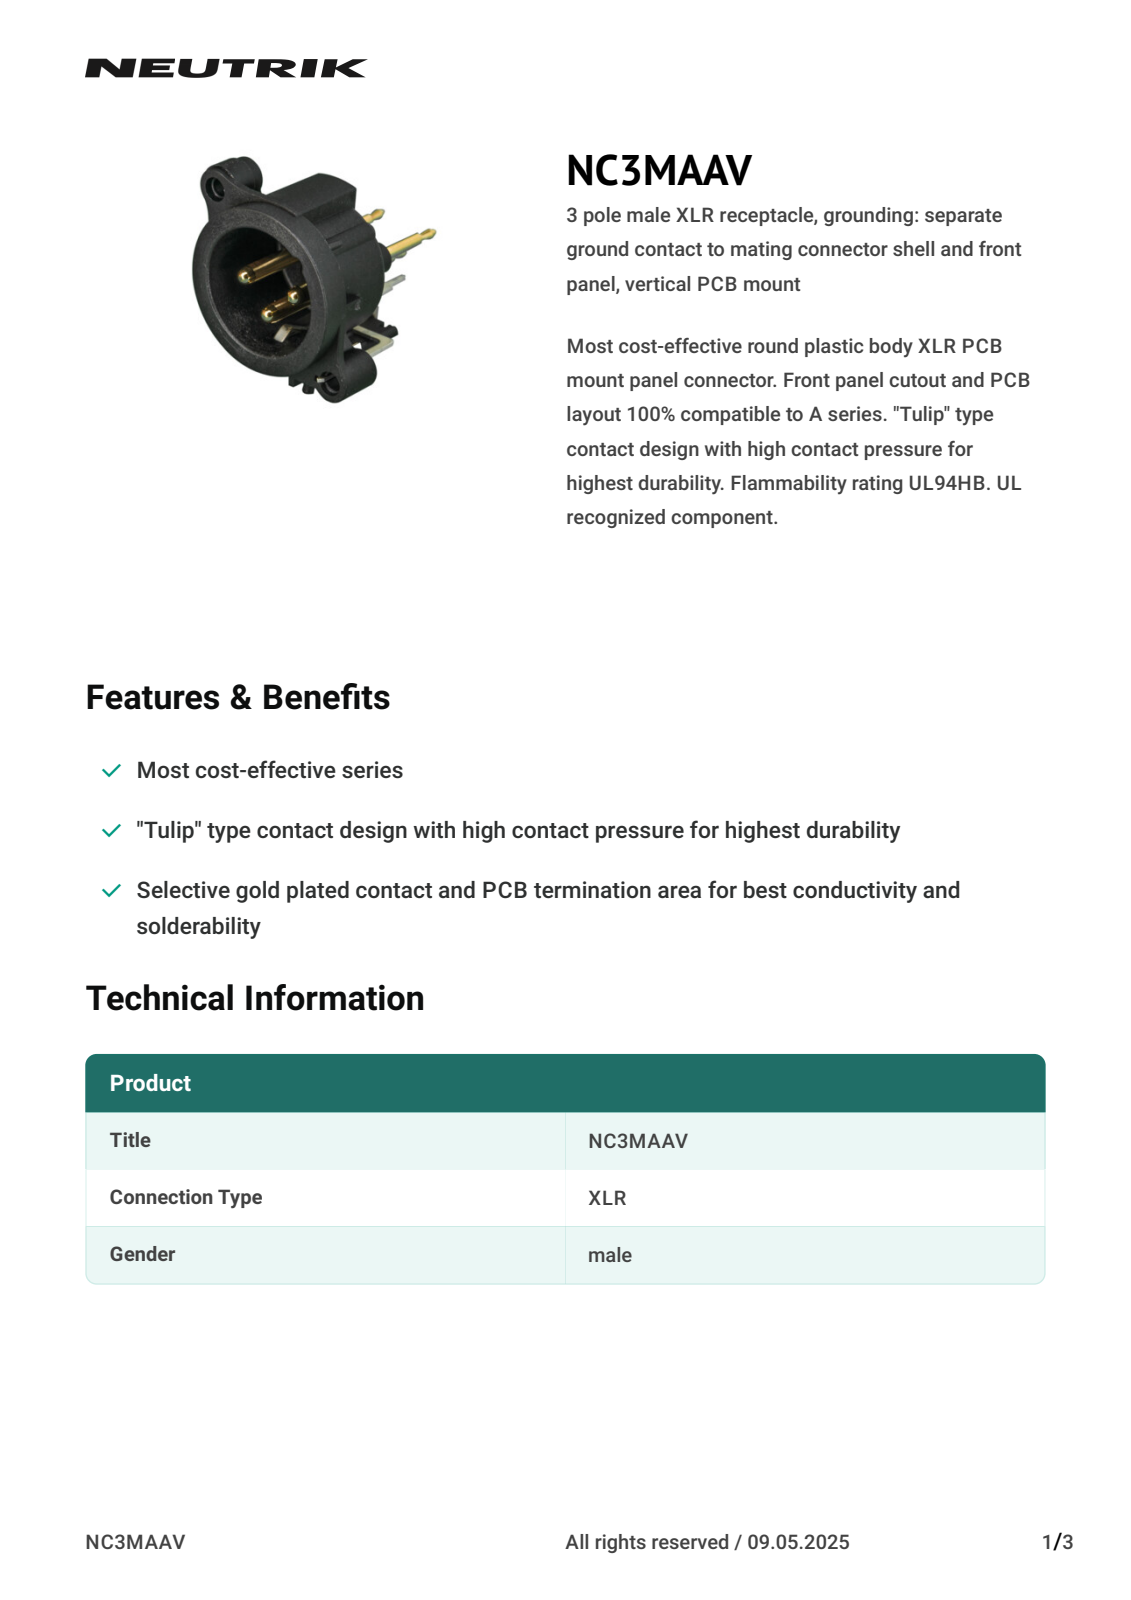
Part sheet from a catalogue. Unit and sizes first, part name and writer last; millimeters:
Units: millimetres
Overall size (bounding box): 30.2 × 27.6 × 25.3
Round holes (diameter × count): ⌀2.25 ×1, ⌀2.35 ×1, ⌀2.5 ×1, ⌀3.2 ×1
Round bosses / shafts (diameter × count): ⌀2.38 ×3, ⌀1.8 ×3, ⌀1.7 ×3, ⌀1 ×3, ⌀1.5 ×2, ⌀21.8 ×1, ⌀5.8 ×1, ⌀5.2 ×1
Partial cylindrical surfaces — rounded edges, fillets, slot ends (radius × count): R0.2 ×39, R0.3 ×29, R0.12 ×9, R0.4 ×7, R0.5 ×6, R1 ×6, R0.75 ×3, R0.9 ×2
Main face-to-face distances: 1.1, 14.5, 13.4, 9.7, 10.8, 3.7, 2.7, 1, 10.7, 11.8
Hole centre spacings: 10.92, 18.14, 28
Volume: 2 591 mm³ · Surface area: 4 186 mm²
Bodies: 1 solid, 744 faces (398 planar, 178 cylindrical, 168 other)
Part name (STEP PRODUCT): 30010620
STEP written by: CREO PARAMETRIC BY PTC INC, 2021184 (CONFIG_CONTROL_DESIGN)
